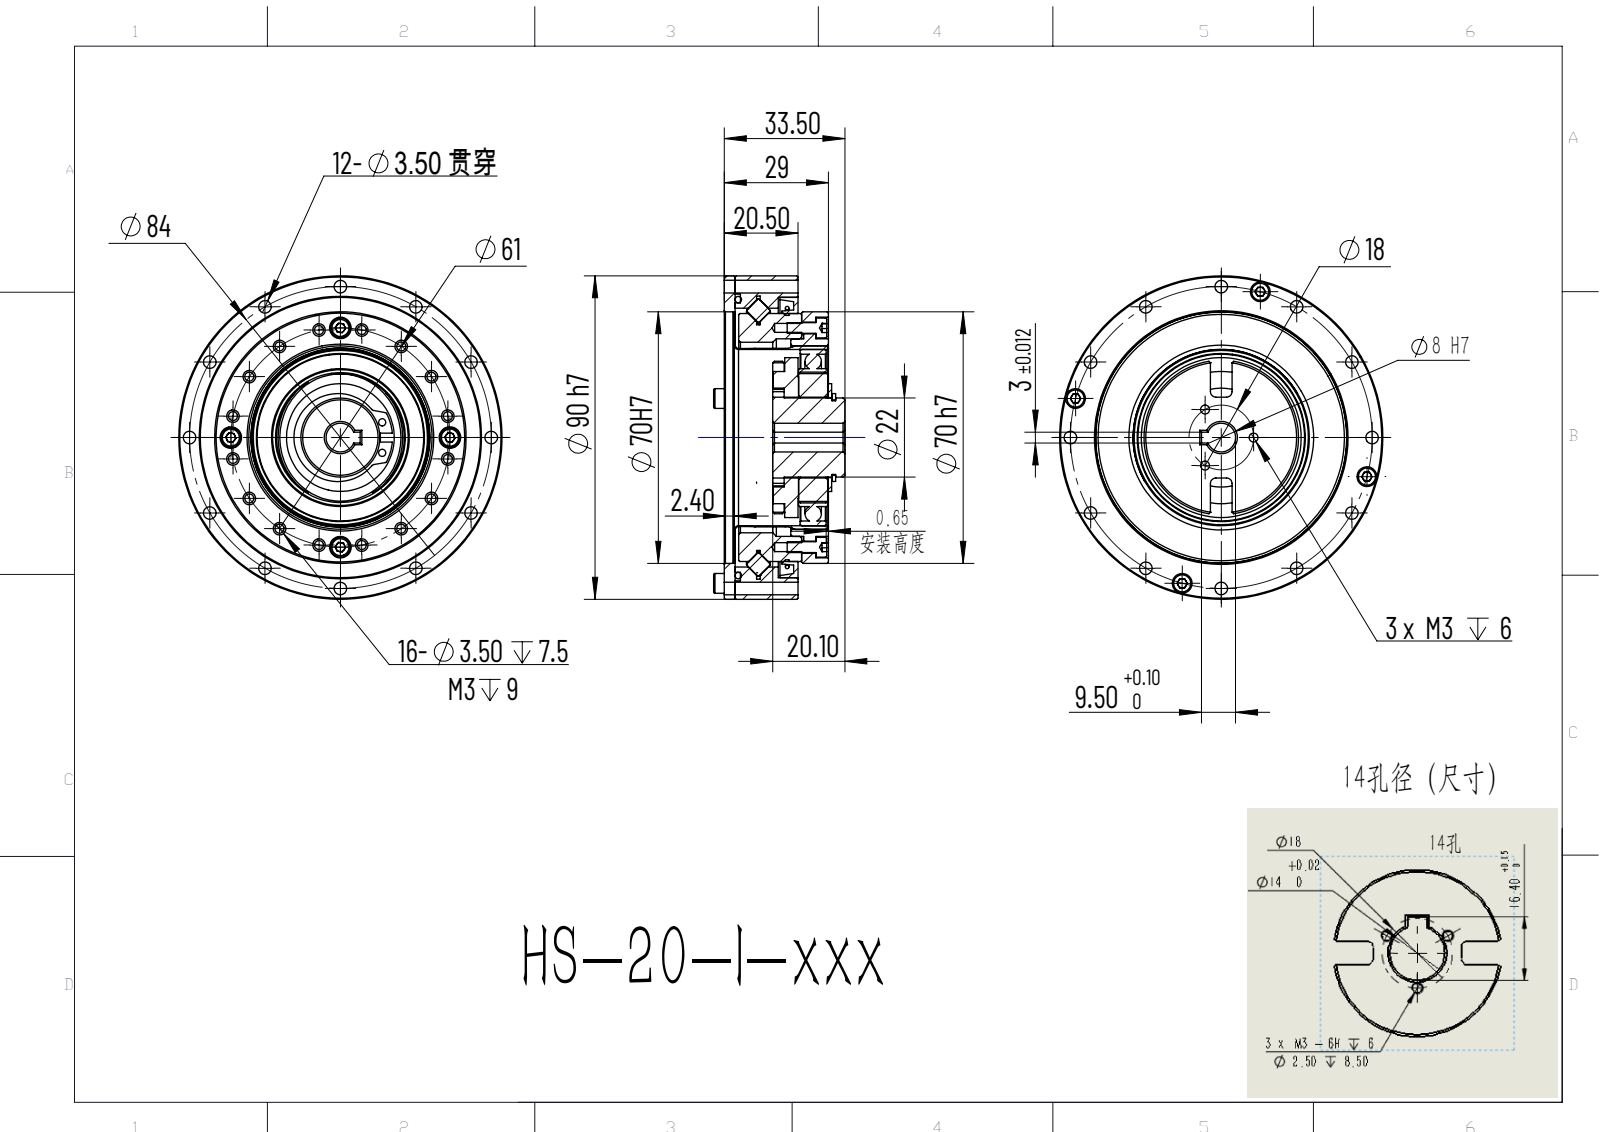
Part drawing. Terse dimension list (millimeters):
name: HS-20-I; hexagon socket head cap screws gb_GB_FASTENER_SCREWS_HSHCS M3X8-C; ????-STXB-20050-01; 20-50??????_?? <1> (+8 more)
written by: ONSHAPE BY PTC INC, 1.201 (AP242_MANAGED_MODEL_BASED_3D_ENGINEERING_MIM_LF)
unit: mm
bodies: 96 solids, 1074 faces (599 planar, 274 cylindrical, 201 other)
size: 90 × 90 × 36.56
volume: 109 276 mm³; area: 91 069 mm²
holes: 32× ⌀3.5, 27× ⌀2.5, 4× ⌀3.4, 4× ⌀6, 2× ⌀2, 1× ⌀2.05, 1× ⌀2.9, 1× ⌀5, 1× ⌀8, 1× ⌀20.5, 1× ⌀22.3, 1× ⌀22.5
bosses: 36× ⌀5, 8× ⌀5.5, 8× ⌀3, 1× ⌀90, 1× ⌀75, 1× ⌀69, 1× ⌀62.8, 1× ⌀51.19
rounds: 36× R2.52, 4× R1.5, 2× R0.5, 2× R1, 2× R12.25, 1× R13.75, 1× R14.5
face distances: 1, 17.5, 4, 16.66, 3, 18.5, 20.5, 21.5, 13.92, 2.74
hole spacings: 42, 21.74, 72.74, 81.13, 30.5, 39.51, 59.39, 59.4
